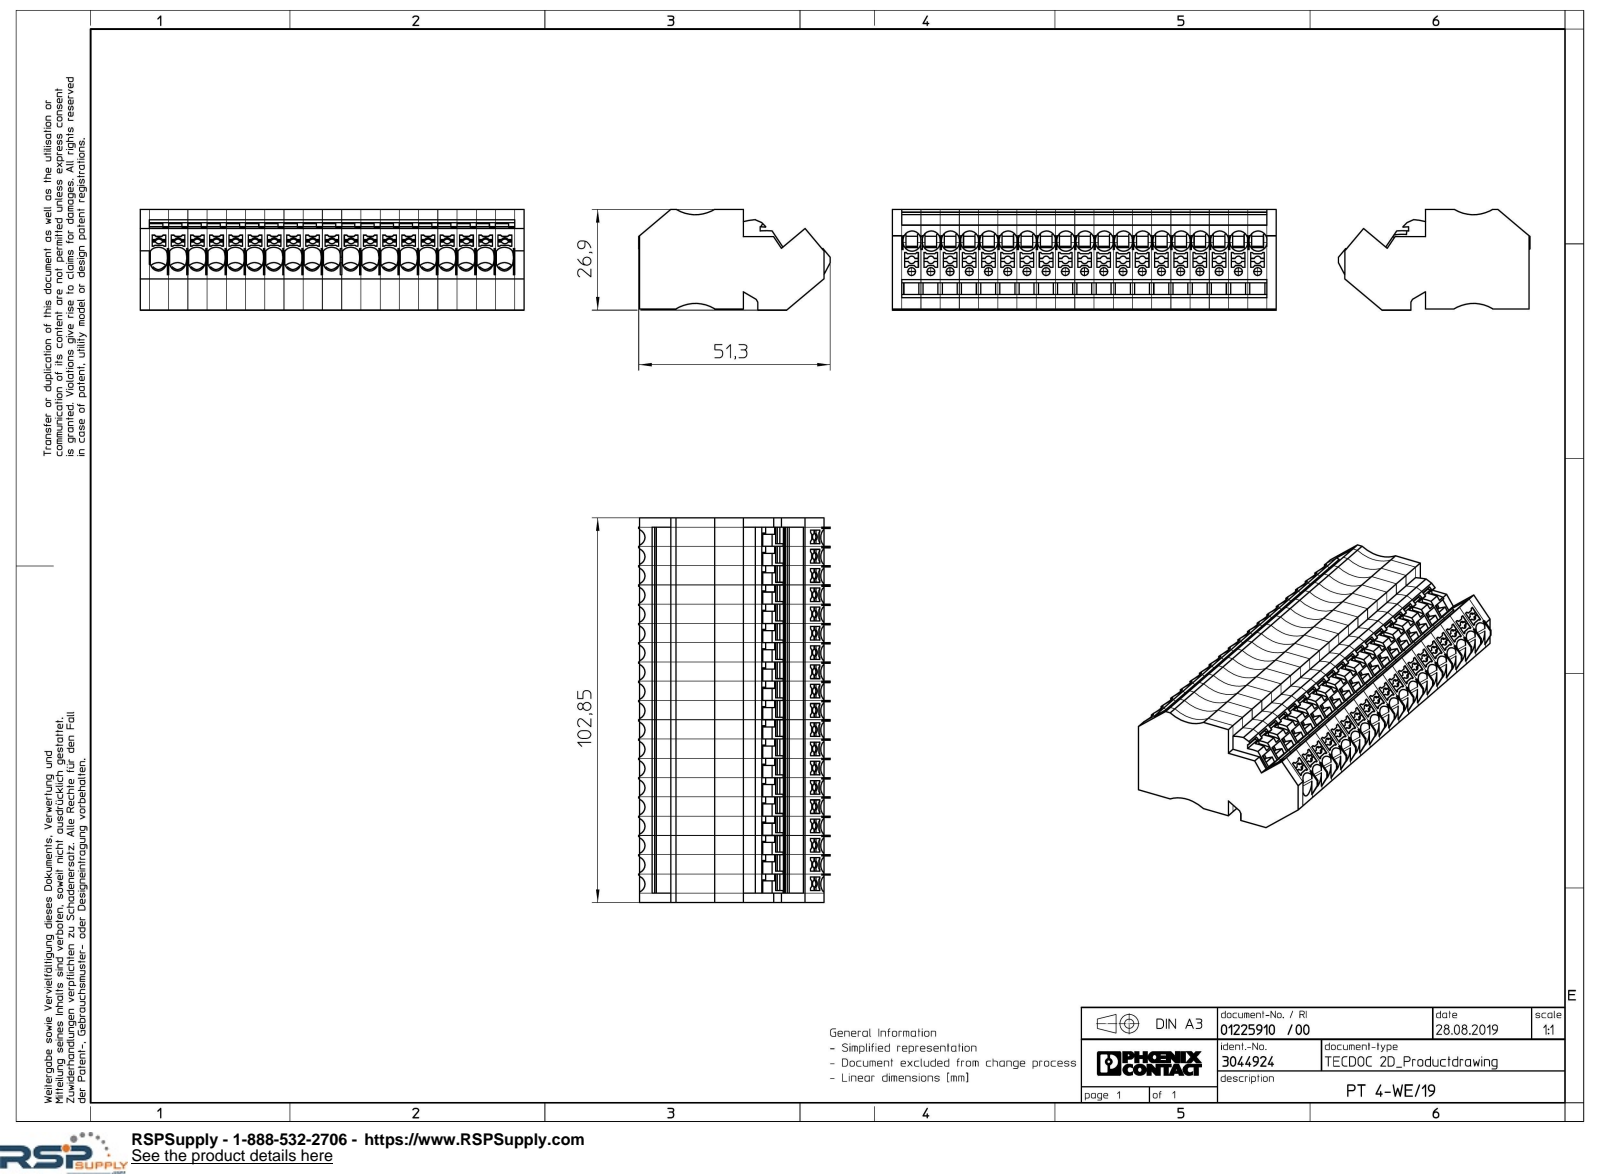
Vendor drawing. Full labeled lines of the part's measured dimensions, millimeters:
Part name (STEP PRODUCT): PT_4_WE_19-select
STEP written by: Creo Elements/Direct Modeling 20.1A 29-Sep-2018 (C) Parametric Technology GmbH (AUTOMOTIVE_DESIGN)
Units: millimetres
Bodies: 1 solid, 3167 faces (2745 planar, 384 cylindrical, 38 other)
Overall size (bounding box): 102.85 × 51.3 × 26.9
Volume: 92 424 mm³ · Surface area: 35 428 mm²
Round holes (diameter × count): ⌀2.1 ×19
Partial cylindrical surfaces — rounded edges, fillets, slot ends (radius × count): R2.4 ×76, R1 ×38, R1.03 ×3, R10 ×2, R1.05 ×1, R1.78 ×1, R12.4 ×1, R13.38 ×1
Main face-to-face distances: 3.15, 3.85, 7, 102.85, 19.6, 26.6, 22.75, 7.3, 27.8, 10.3
Hole centre spacings: 5.15, 10.3, 15.45, 20.6, 25.75, 30.9, 36.05, 41.2
